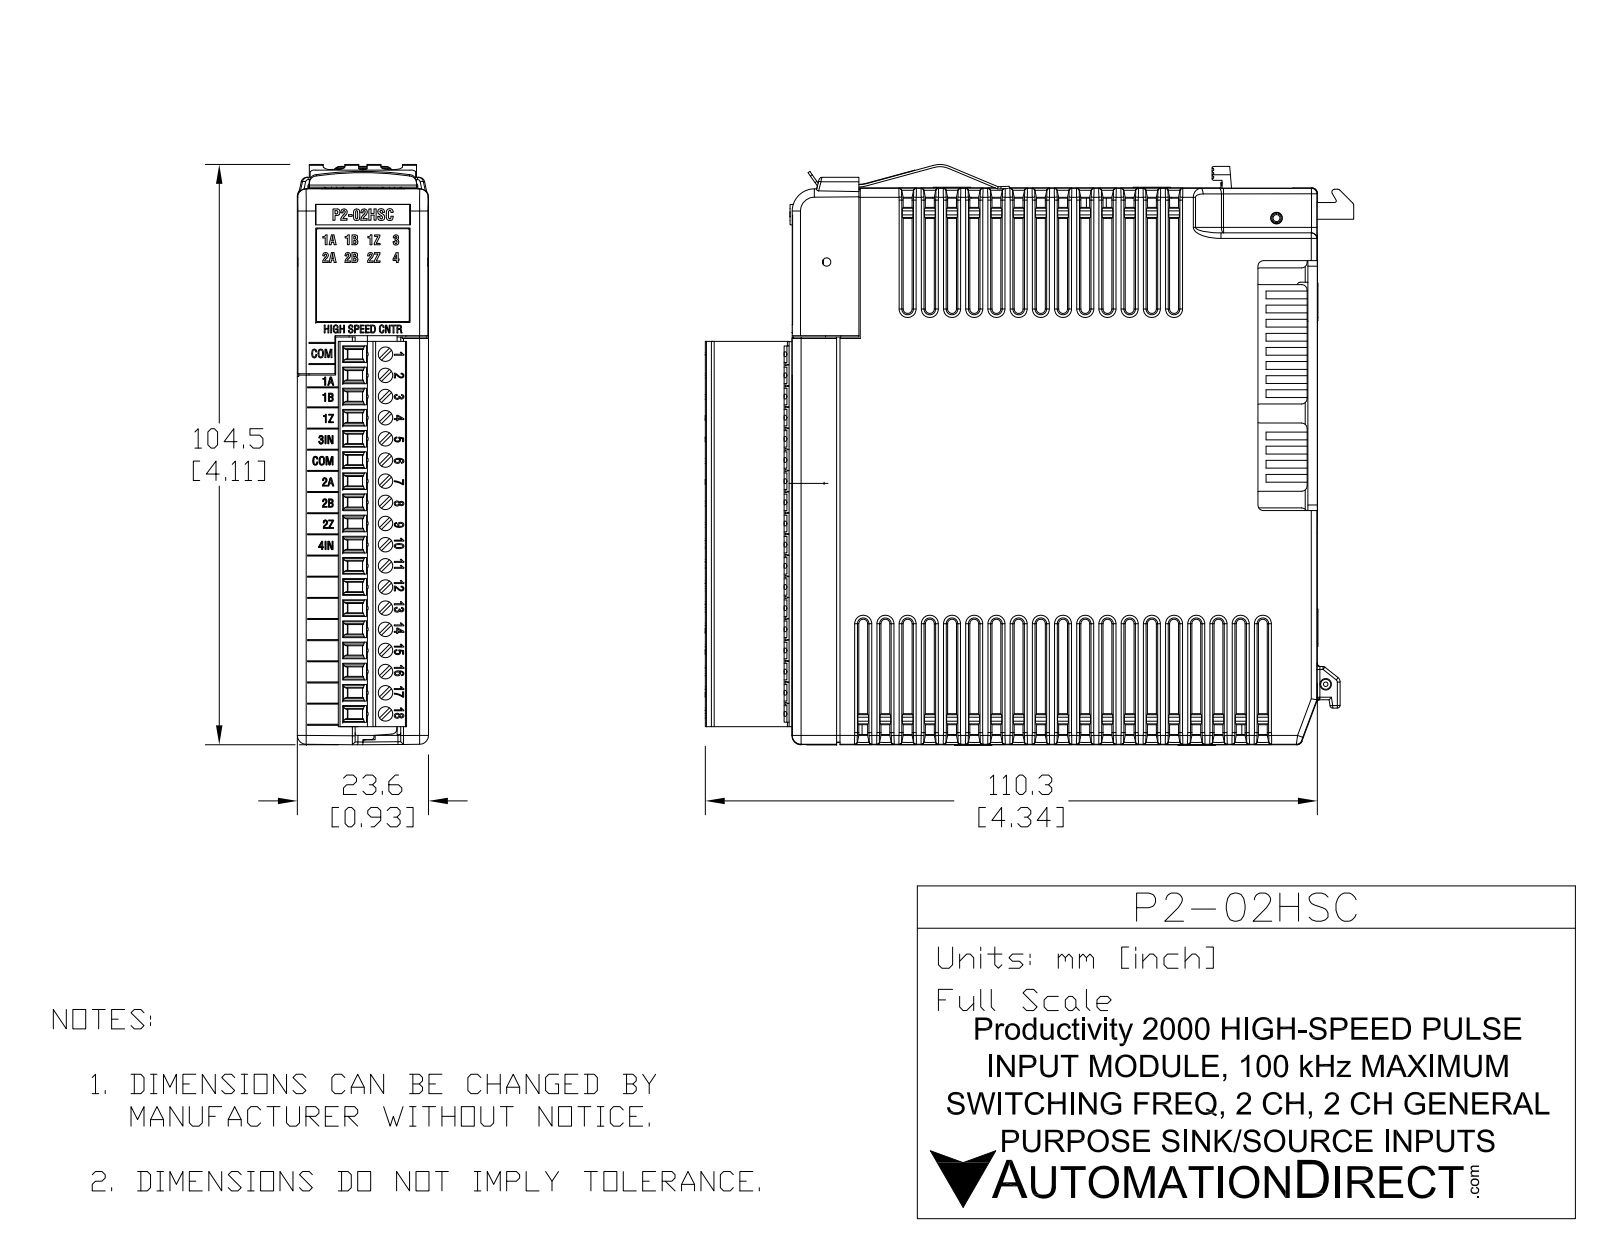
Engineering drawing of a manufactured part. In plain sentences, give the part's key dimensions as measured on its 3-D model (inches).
The part is named "P2-02HSC red 1B 2 comb 2 Coord Bb fXT EXT Comb fXT wc". Its 3-D file was written by "SolidWorks 2017 (AUTOMOTIVE_DESIGN)". It is 2 solids with 3076 faces: 2028 planar, 483 cylindrical and 565 other. Overall it measures 4.104 by 4.004 by 0.93 inches. Its volume is 12.13 cubic inches and its surface area 68.51 square inches. Round holes: 2 of diameter 0.049, 1 of diameter 0.059, 1 of diameter 0.079, 1 of diameter 0.083, 1 of diameter 0.098. Partial cylindrical surfaces (rounded edges, fillets, slot ends): 150 of radius 0.02, 87 of radius 0.008, 73 of radius 0.039, 18 of radius 0.062, 13 of radius 0.063, 9 of radius 0.012, 6 of radius 0.059, 6 of radius 0.079. The main face-to-face distances are 0.93, 0.063, 0.867, 3.594, 0.12, 3.474, 0.222, 0.59, 2.884, 3.004. The hole center spacings are 0.62, 3.206, 3.206.
